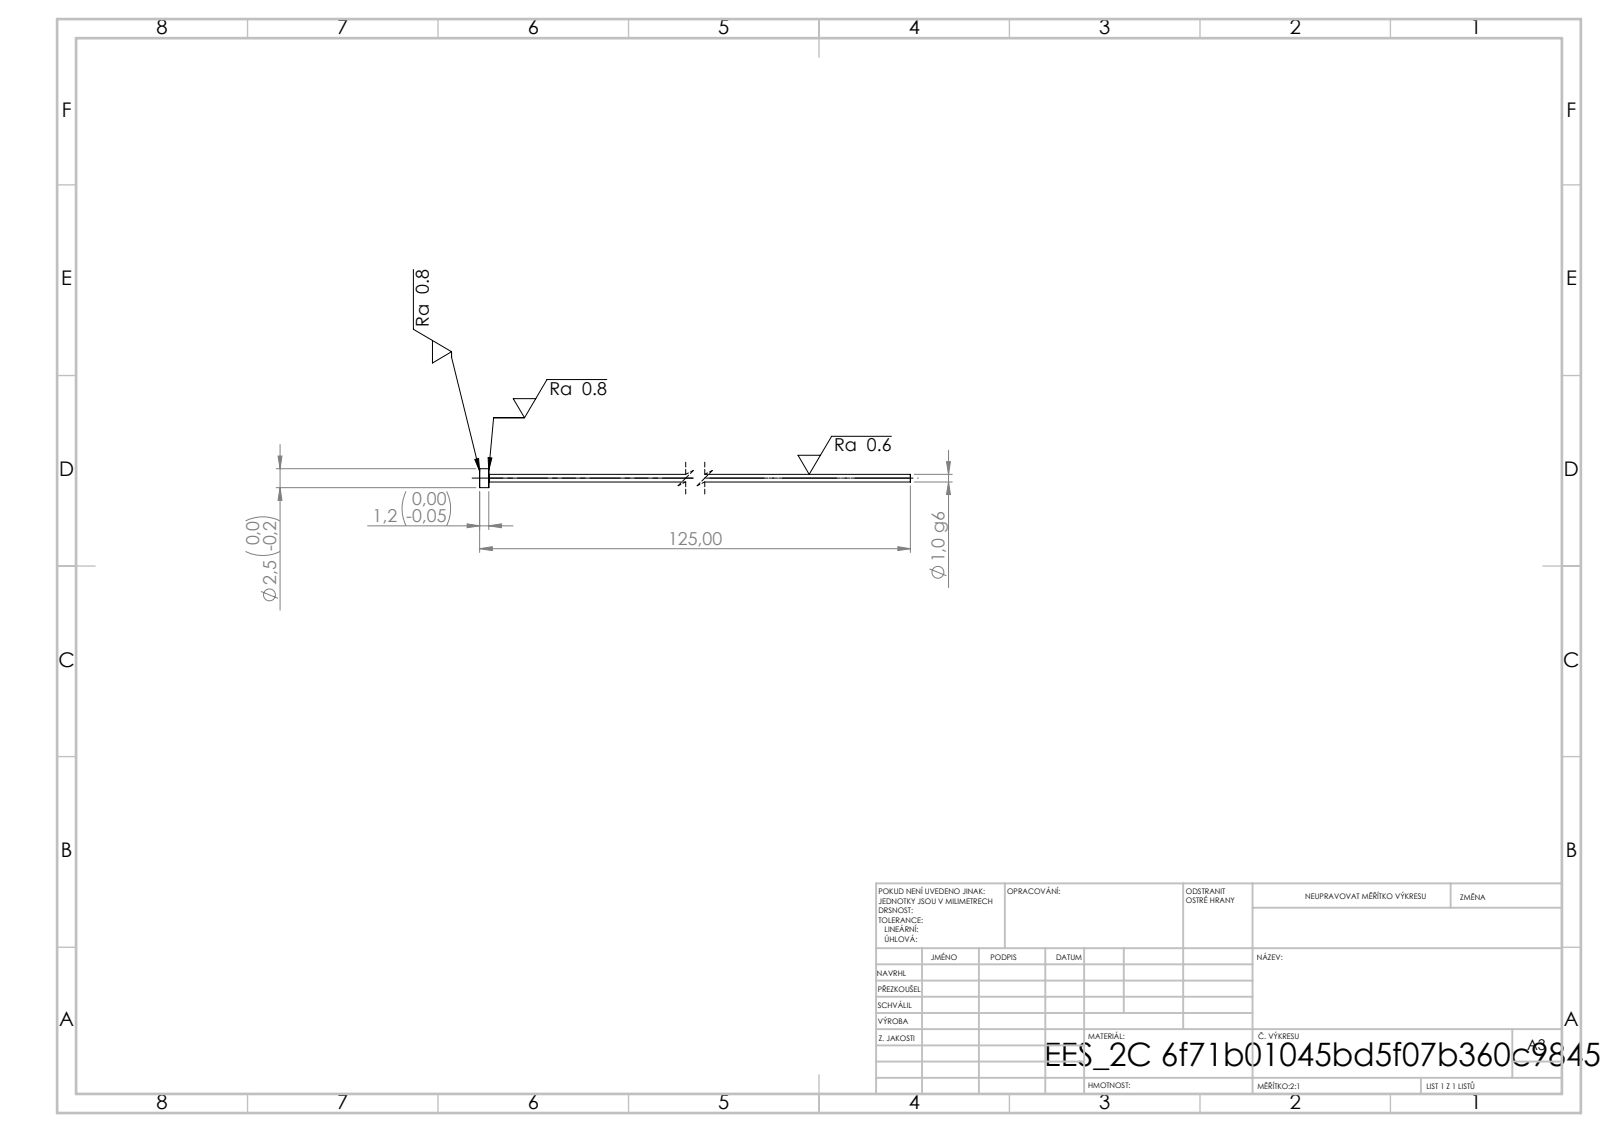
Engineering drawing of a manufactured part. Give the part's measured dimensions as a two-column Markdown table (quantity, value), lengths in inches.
| quantity | value |
| --- | --- |
| STEP written by | SolidWorks 2019 (CONFIG_CONTROL_DESIGN) |
| units | inches |
| bodies | 1 solid, 7 faces (3 planar, 4 cylindrical, 0 other) |
| overall size | 4.921 × 0.098 × 0.098 |
| volume | 0.006 in³ |
| surface area | 0.632 in² |
| round bosses / shafts (diameter × count) | 0.098 × 1, 0.039 × 1 |
| main face-to-face distances | 0.047, 4.921, 4.874 |
